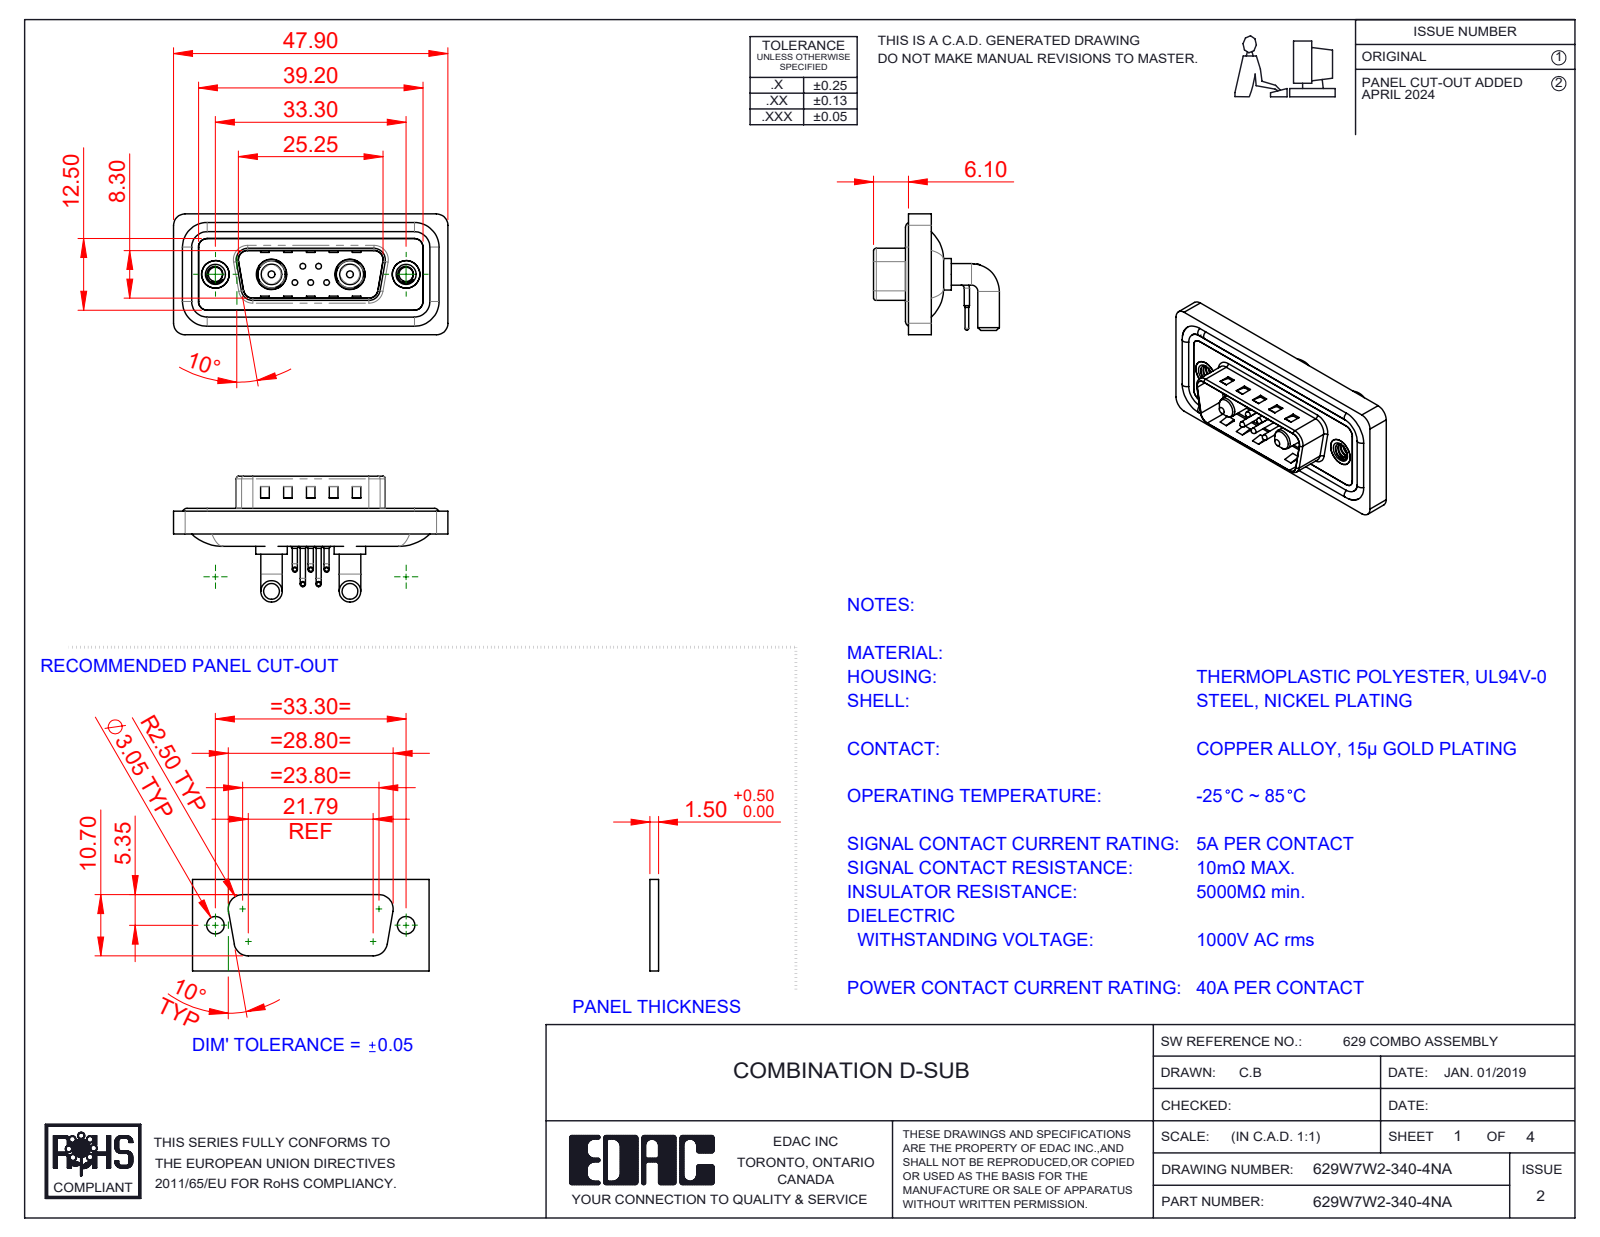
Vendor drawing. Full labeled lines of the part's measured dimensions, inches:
Part name (STEP PRODUCT): 629Combo Contact Row 2; 629Combo Shell Front_15 Contacts; 629W7W2-340-4NA; Power Pin_40A RA (+5 more)
STEP written by: SolidWorks 2023 (CONFIG_CONTROL_DESIGN)
Units: inches
Bodies: 16 solids, 1077 faces (517 planar, 404 cylindrical, 156 other)
Overall size (bounding box): 1.886 × 0.865 × 0.831
Volume: 0.356 in³ · Surface area: 14.31 in²
Round holes (diameter × count): ⌀0.03 ×5, ⌀0.063 ×5, ⌀0.079 ×5, ⌀0.098 ×2, ⌀0.157 ×2, ⌀0.189 ×2, ⌀0.191 ×2, ⌀0.197 ×2, ⌀0.209 ×2
Round bosses / shafts (diameter × count): ⌀0.035 ×10, ⌀0.059 ×5, ⌀0.039 ×5, ⌀0.026 ×5, ⌀0.148 ×4, ⌀0.063 ×4, ⌀0.217 ×2, ⌀0.205 ×2
Partial cylindrical surfaces — rounded edges, fillets, slot ends (radius × count): R0.079 ×20, R0.059 ×18, R0.02 ×8, R0.063 ×8, R0.04 ×5, R0.01 ×4, R0.024 ×4, R0.026 ×4
Main face-to-face distances: 0.016, 0.114, 0.031, 0.043, 0.083, 0.063, 0.098, 0.122, 0.177, 0.161
Hole centre spacings: 0.124, 0.109, 0.386, 0.925, 0.17, 0.17, 0.198, 0.198
